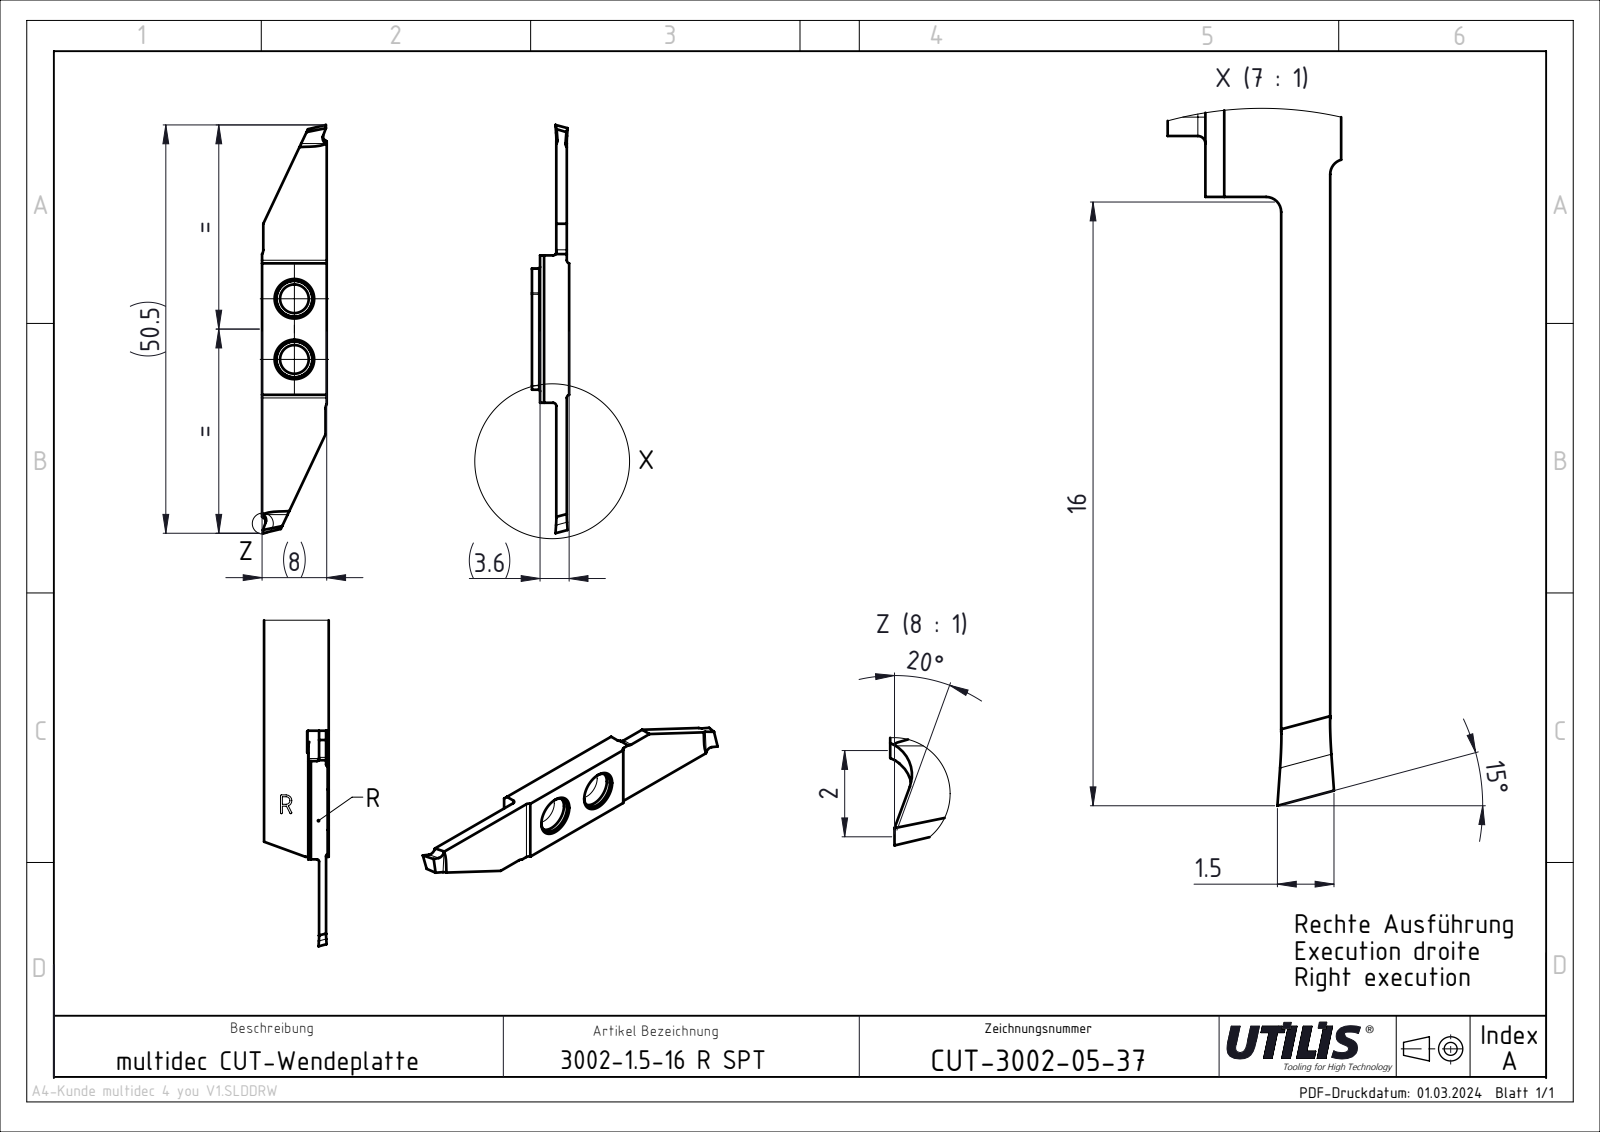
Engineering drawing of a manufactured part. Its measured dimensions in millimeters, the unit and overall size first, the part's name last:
Units: millimetres
Overall size (bounding box): 50.5 × 8 × 3.6
Round holes (diameter × count): ⌀3.55 ×2
Partial cylindrical surfaces — rounded edges, fillets, slot ends (radius × count): R0.4 ×4, R1 ×2
Main face-to-face distances: 1.3, 1.59, 2.01, 3.31, 3.6, 8, 18.09, 18.22, 7.85, 1.1
Hole centre spacings: 7.5
Volume: 683 mm³ · Surface area: 941 mm²
Bodies: 1 solid, 32 faces (22 planar, 10 cylindrical, 0 other)
Part name (STEP PRODUCT): CUT-3002 SPT Slim_and_Deep; ASME Y14.5
STEP written by: SolidWorks 2023 SP4 || FormatWorks Professional (AP242_MANAGED_MODEL_BASED_3D_ENGINEERING_MIM_LF)
